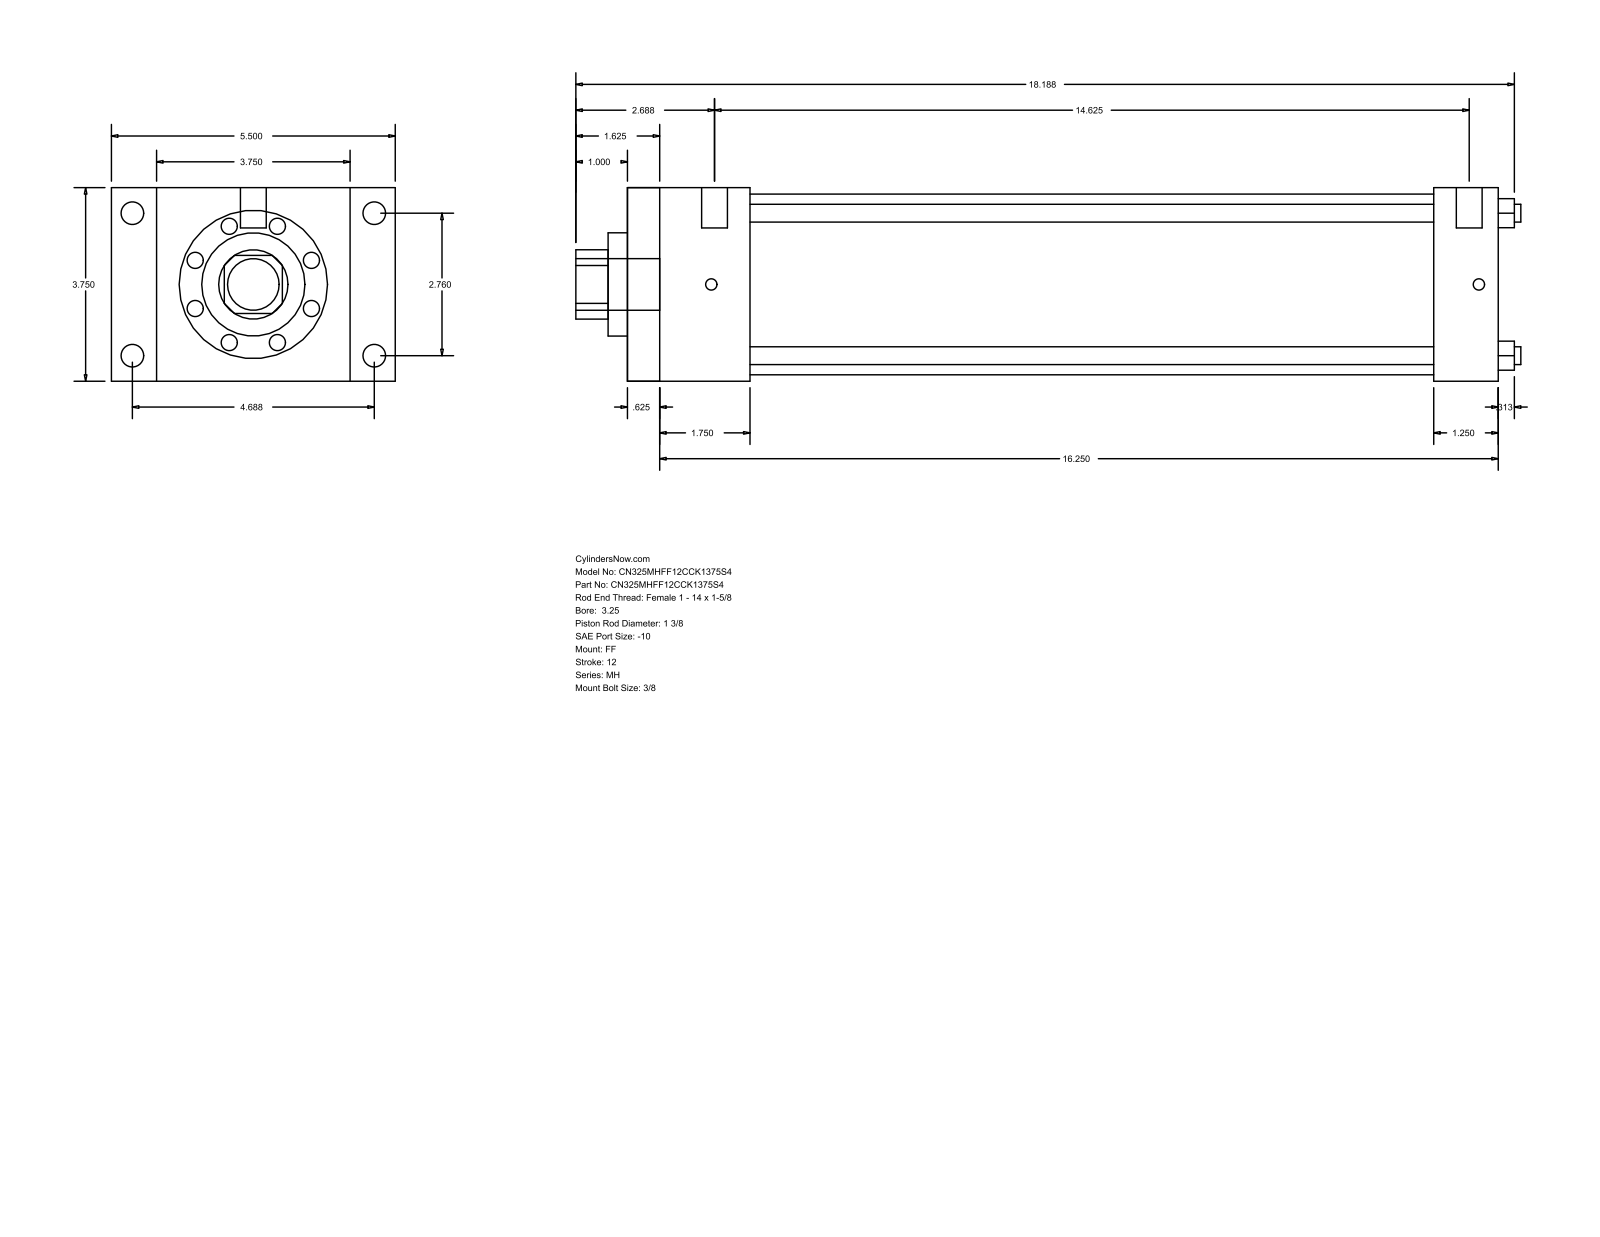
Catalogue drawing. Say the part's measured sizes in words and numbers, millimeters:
The part is named "MH_FF__0325_1.375". Its 3-D file was written by "GSSL Pune (CONFIG_CONTROL_DESIGN)". It is 0 solids with 92 faces: 64 planar, 28 cylindrical and 0 other. Overall it measures 465.14 by 139.7 by 95.25 millimeters. Round holes: 4 of diameter 8.76, 1 of diameter 34.92, 1 of diameter 50.8, 1 of diameter 88.9. Round bosses or shafts: 4 of diameter 11.13, 4 of diameter 5.56, 2 of diameter 12.7, 1 of diameter 25.4. Partial cylindrical surfaces (rounded edges, fillets, slot ends): 1 of radius 17.06. The main face-to-face distances are 95.24, 428.62, 15.87, 412.75, 22.23, 117.47, 396.87, 381, 31.75, 60.32. The hole center spacings are 49.57, 70.1, 99.14.
